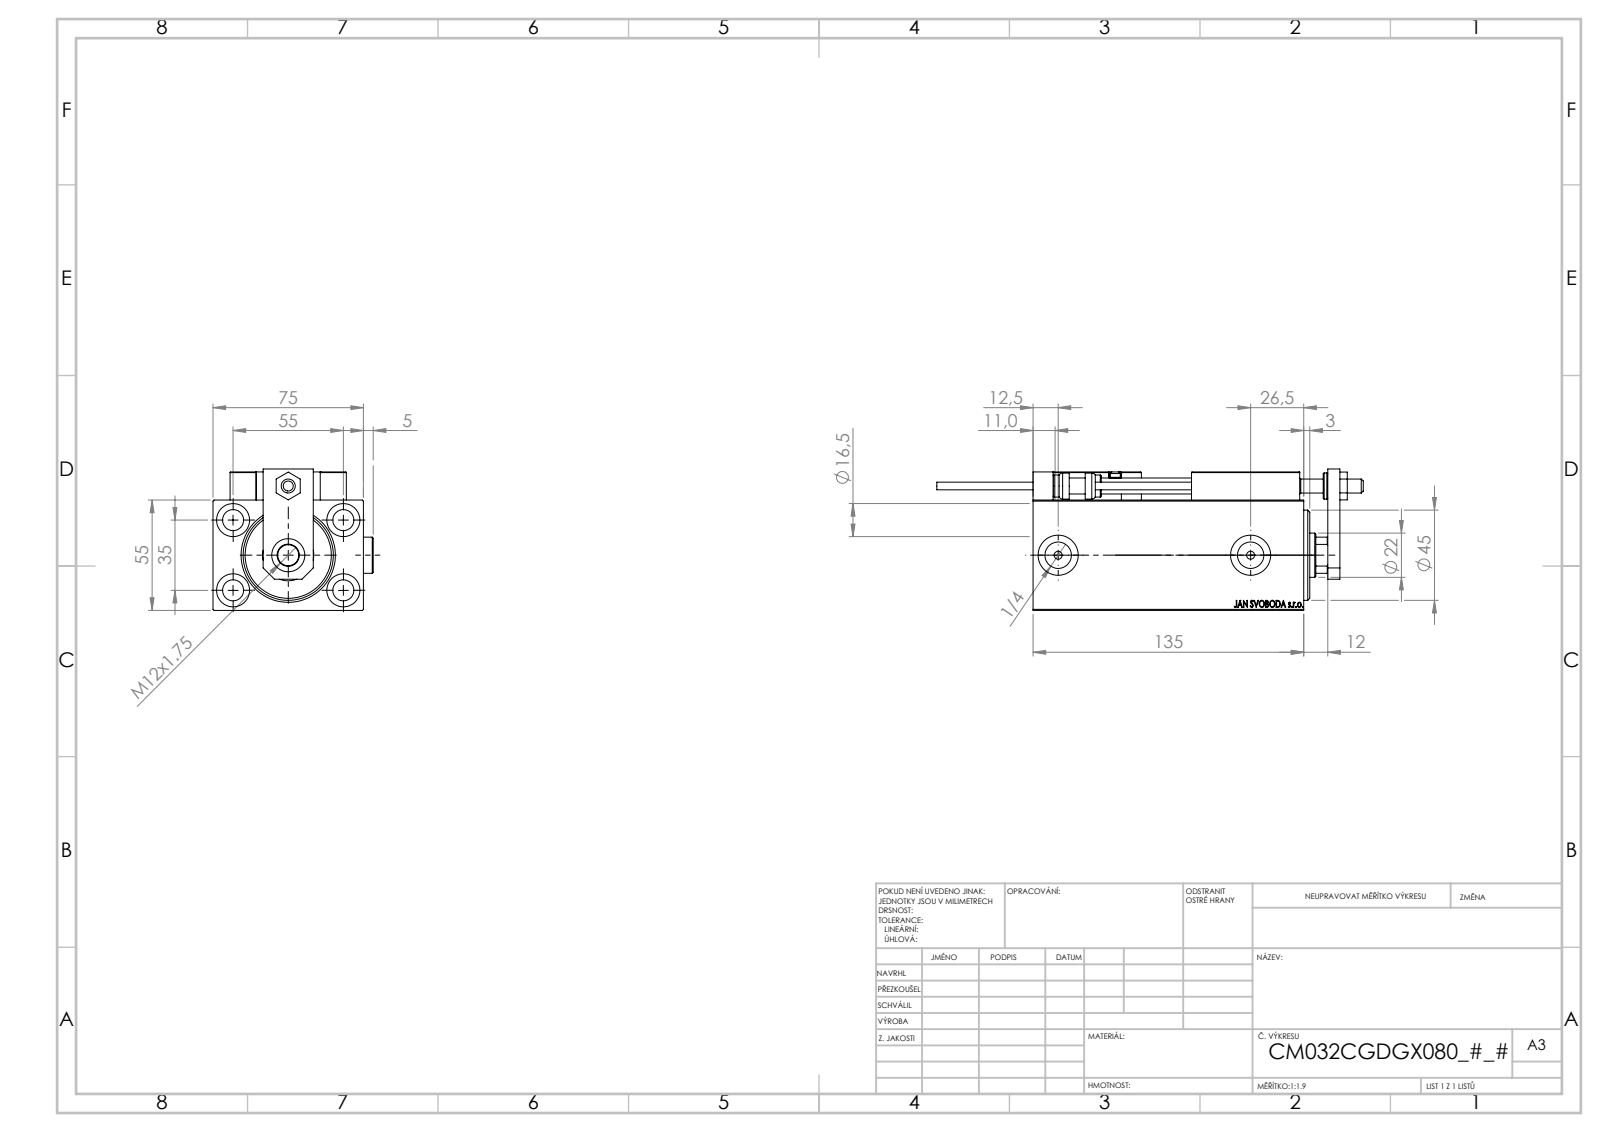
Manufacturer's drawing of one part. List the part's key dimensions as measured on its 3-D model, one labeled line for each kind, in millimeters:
Part name (STEP PRODUCT): KONCOVKA; SWITCH X; ALLEN BOLT D8; SWITCH_X_FRONT_BACK (+7 more)
STEP written by: SolidWorks 2019 (CONFIG_CONTROL_DESIGN)
Units: millimetres
Bodies: 25 solids, 1336 faces (594 planar, 204 cylindrical, 538 other)
Overall size (bounding box): 212.7 × 79.9 × 70.5
Volume: 515 953 mm³ · Surface area: 122 553 mm²
Round holes (diameter × count): ⌀4 ×6, ⌀8 ×5, ⌀10.5 ×5, ⌀16.5 ×5, ⌀3.2 ×4, ⌀5 ×2, ⌀13.16 ×2, ⌀20 ×2, ⌀7 ×1, ⌀22 ×1, ⌀25.5 ×1, ⌀32 ×1
Round bosses / shafts (diameter × count): ⌀18 ×2, ⌀5 ×2, ⌀3.8 ×2, ⌀13 ×1, ⌀11 ×1
Partial cylindrical surfaces — rounded edges, fillets, slot ends (radius × count): R0.3 ×30, R3 ×2, R10.5 ×1
Main face-to-face distances: 55, 75, 14, 10, 12, 69, 5, 7, 25, 15
Hole centre spacings: 32.6, 11.37, 20, 29.59, 29.69, 32.33, 35, 36.06
